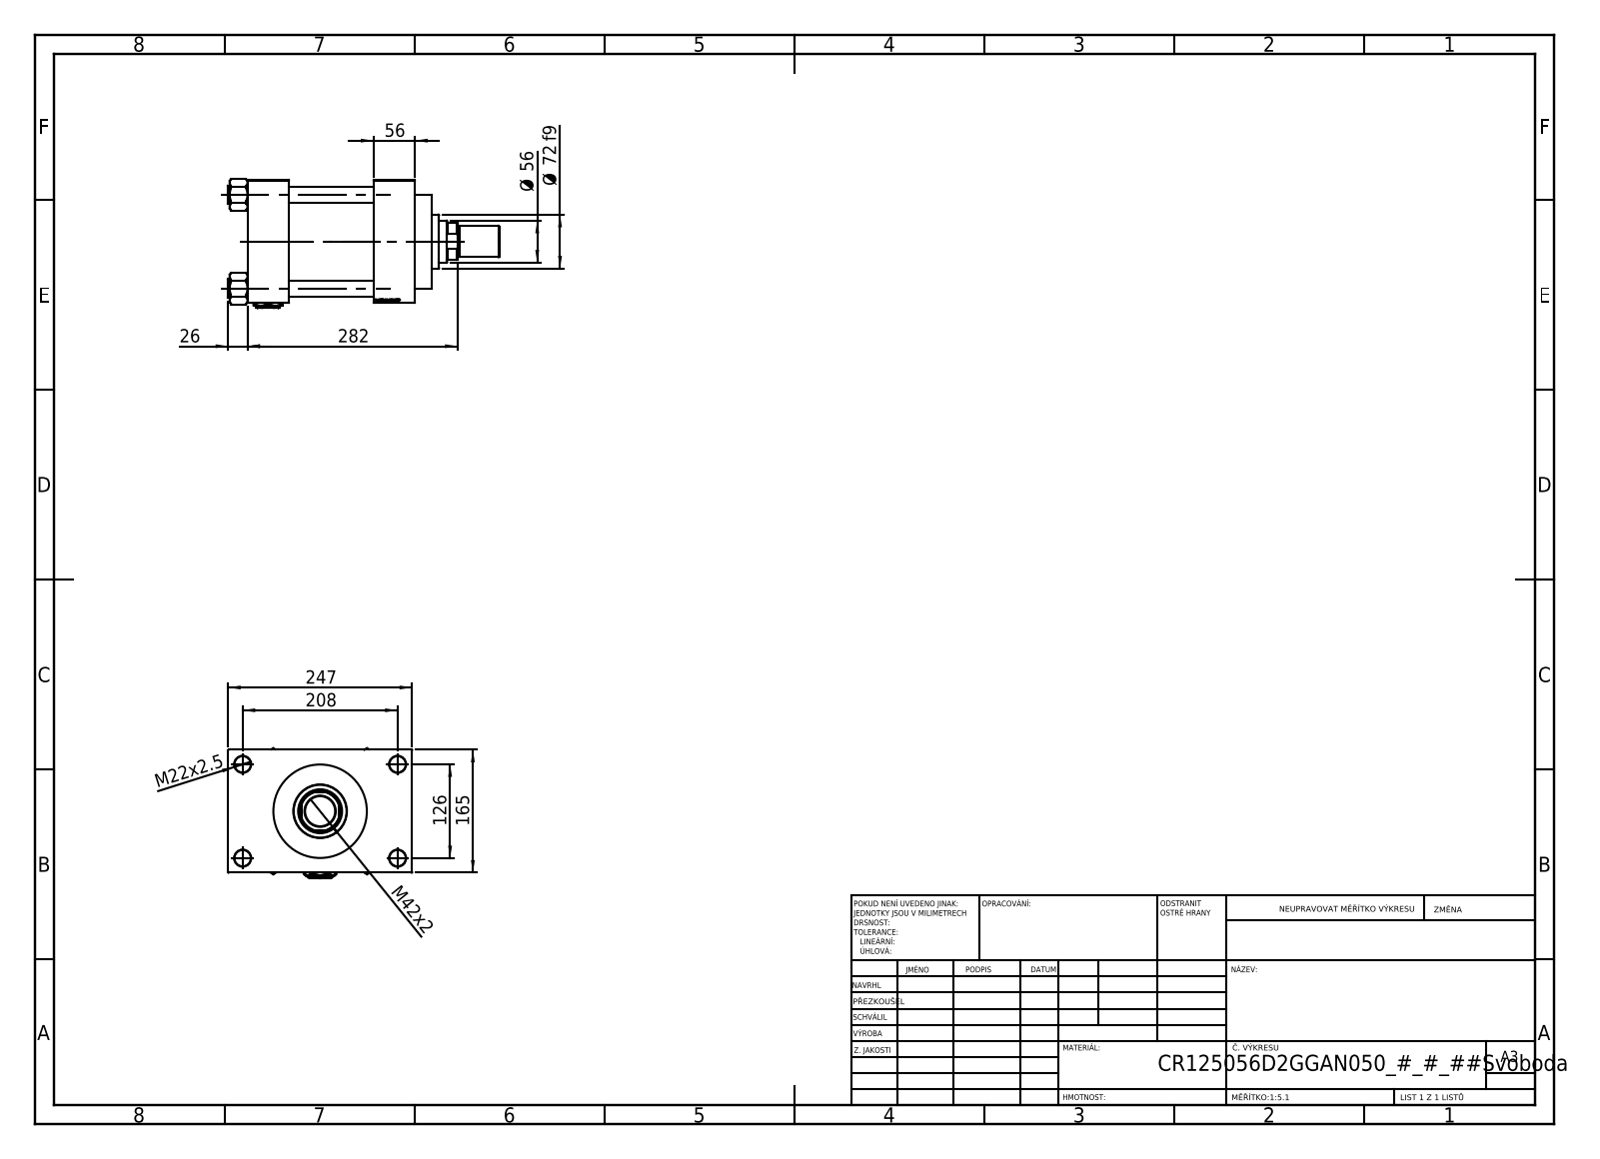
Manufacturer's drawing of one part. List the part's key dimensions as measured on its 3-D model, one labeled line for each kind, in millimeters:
Part name (STEP PRODUCT): V215CR_VCP_D; V215_VC_A; V215CR_D_Body; NUT_M5_D (+3 more)
STEP written by: SolidWorks 2019 (CONFIG_CONTROL_DESIGN)
Units: millimetres
Bodies: 13 solids, 1216 faces (572 planar, 98 cylindrical, 546 other)
Overall size (bounding box): 364 × 247 × 174.07
Volume: 5 187 000 mm³ · Surface area: 583 761 mm²
Round holes (diameter × count): ⌀22 ×8, ⌀7 ×2, ⌀32.24 ×2, ⌀45 ×2, ⌀40.5 ×1, ⌀56 ×1, ⌀59 ×1, ⌀96 ×1, ⌀125 ×1, ⌀125.5 ×1
Round bosses / shafts (diameter × count): ⌀25 ×4, ⌀131 ×1, ⌀72 ×1, ⌀42 ×1, ⌀40 ×1
Partial cylindrical surfaces — rounded edges, fillets, slot ends (radius × count): R27 ×1
Main face-to-face distances: 169, 114, 165, 55, 56, 170, 225, 41, 206, 247
Hole centre spacings: 41.05, 89.02, 121.59, 125.9, 132.47, 166.95, 209.13, 126
